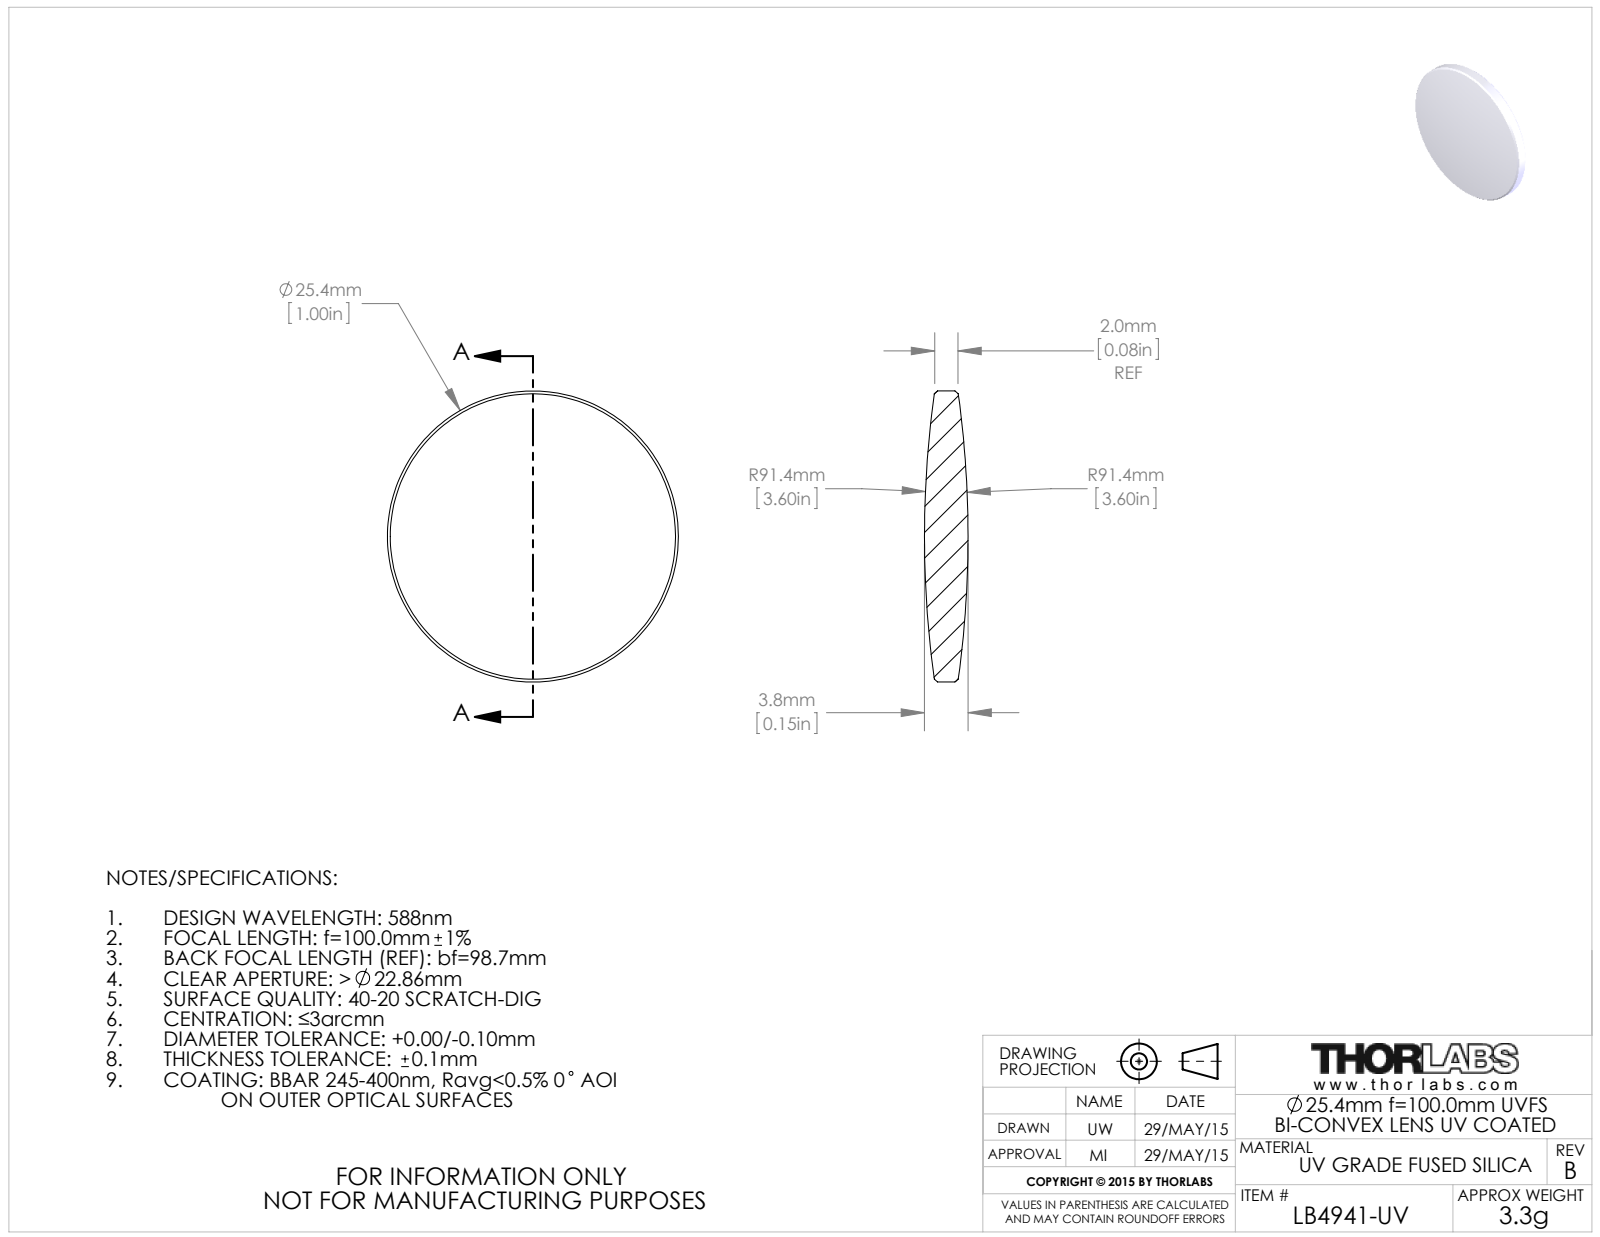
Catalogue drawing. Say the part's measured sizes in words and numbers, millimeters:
The part is named "4321-E0W". Its 3-D file was written by "SolidWorks 2014 (CONFIG_CONTROL_DESIGN)". It is 1 solid with 10 faces: 0 planar, 2 cylindrical and 8 other. Overall it measures 25.4 by 25.4 by 3.8 millimeters. Its volume is 1 472 cubic millimeters and its surface area 1 160 square millimeters. Round bosses or shafts: 1 of diameter 25.4.
